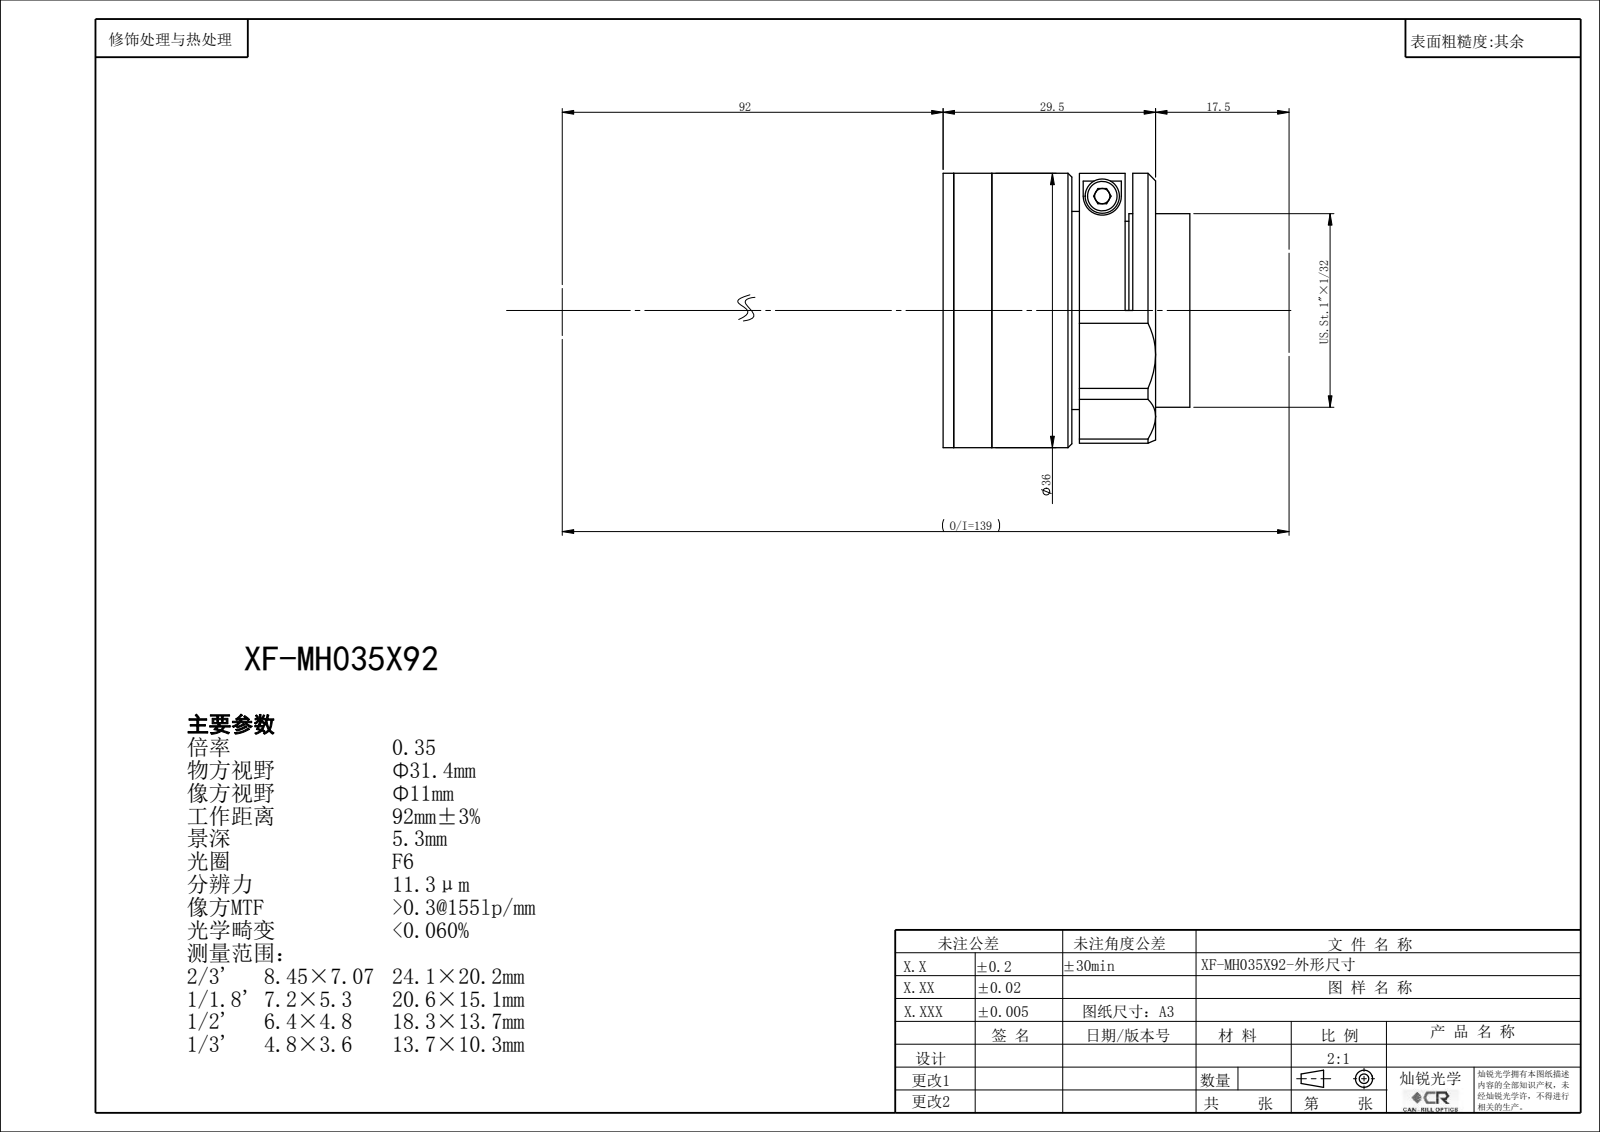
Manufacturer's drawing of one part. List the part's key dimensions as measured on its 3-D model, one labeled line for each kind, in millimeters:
Part name (STEP PRODUCT): XF-MH035X92
STEP written by: SolidWorks 2014 (CONFIG_CONTROL_DESIGN)
Units: millimetres
Bodies: 3 solids, 150 faces (57 planar, 72 cylindrical, 21 other)
Overall size (bounding box): 36 × 36 × 32.4
Volume: 20 547 mm³ · Surface area: 14 148 mm²
Round holes (diameter × count): ⌀2.05 ×1, ⌀3 ×1, ⌀8 ×1, ⌀9 ×1, ⌀10.4 ×1, ⌀13 ×1, ⌀17 ×1, ⌀21 ×1, ⌀24.9 ×1, ⌀26 ×1, ⌀29.4 ×1, ⌀30 ×1
Round bosses / shafts (diameter × count): ⌀36 ×1, ⌀28 ×1, ⌀25.4 ×1, ⌀23.4 ×1, ⌀20 ×1, ⌀4.5 ×1, ⌀2.5 ×1
Partial cylindrical surfaces — rounded edges, fillets, slot ends (radius × count): R25 ×5, R2.5 ×1
Main face-to-face distances: 2, 8.5, 18.14, 15.5, 7, 5, 4.64, 1.4, 10, 2.64
